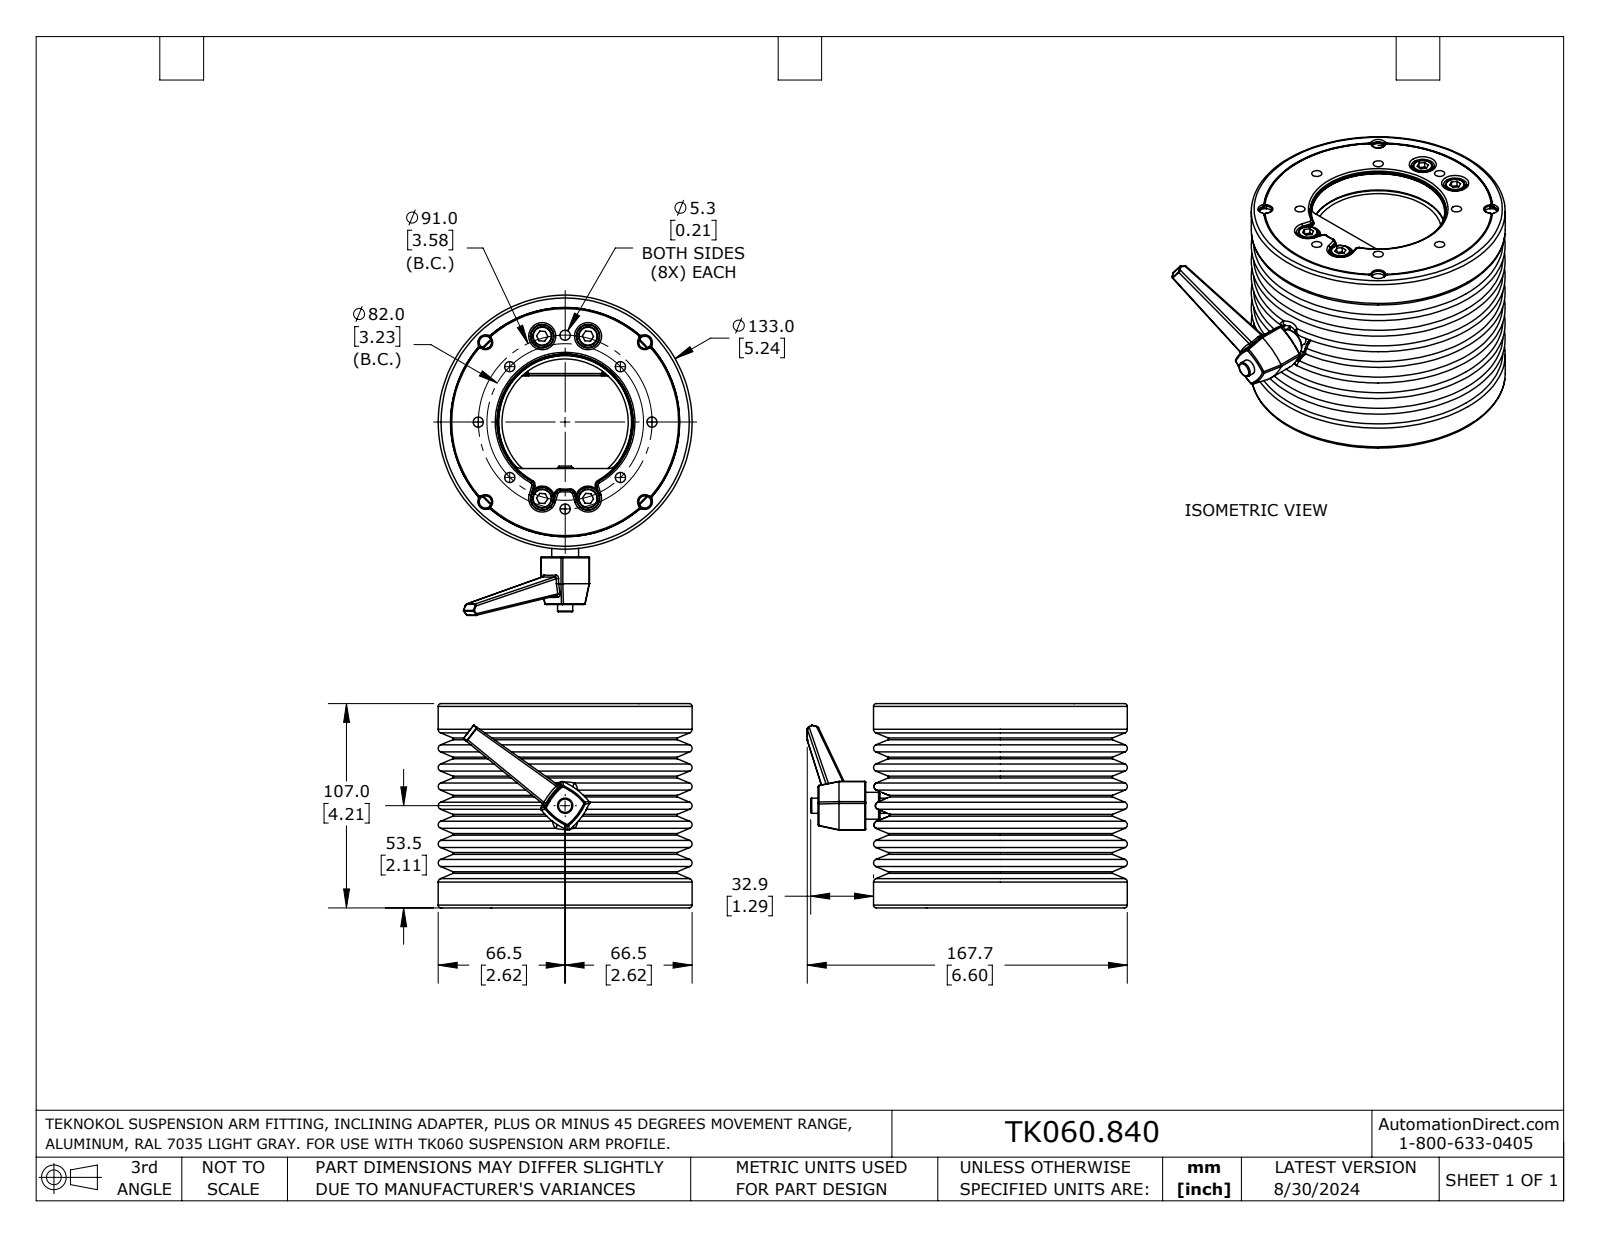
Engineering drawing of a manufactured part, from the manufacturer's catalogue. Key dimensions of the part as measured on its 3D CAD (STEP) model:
Part name (STEP PRODUCT): TK060.840
STEP written by: SolidWorks 2023 (AUTOMOTIVE_DESIGN)
Units: inches
Bodies: 2 solids, 1206 faces (197 planar, 194 cylindrical, 815 other)
Overall size (bounding box): 6.602 × 5.236 × 4.213
Volume: 42.88 in³ · Surface area: 366 in²
Round holes (diameter × count): ⌀0.209 ×4, ⌀0.238 ×3, ⌀2.603 ×1, ⌀4.724 ×1, ⌀5.118 ×1
Round bosses / shafts (diameter × count): ⌀0.394 ×8, ⌀5.236 ×1, ⌀4.543 ×1, ⌀0.556 ×1, ⌀0.315 ×1
Partial cylindrical surfaces — rounded edges, fillets, slot ends (radius × count): R0.039 ×41, R0.059 ×39, R0.01 ×18, R0.02 ×8, R0.016 ×7, R0.157 ×4, R1.346 ×4, R0.335 ×1
Main face-to-face distances: 0.394, 3.543, 3.957, 0.02, 0.413, 3.563, 3.15, 3.976, 0.039, 0.059
Hole centre spacings: 1.314, 3.148, 1.615, 2.283, 1.791, 2.533, 3.229, 3.583
